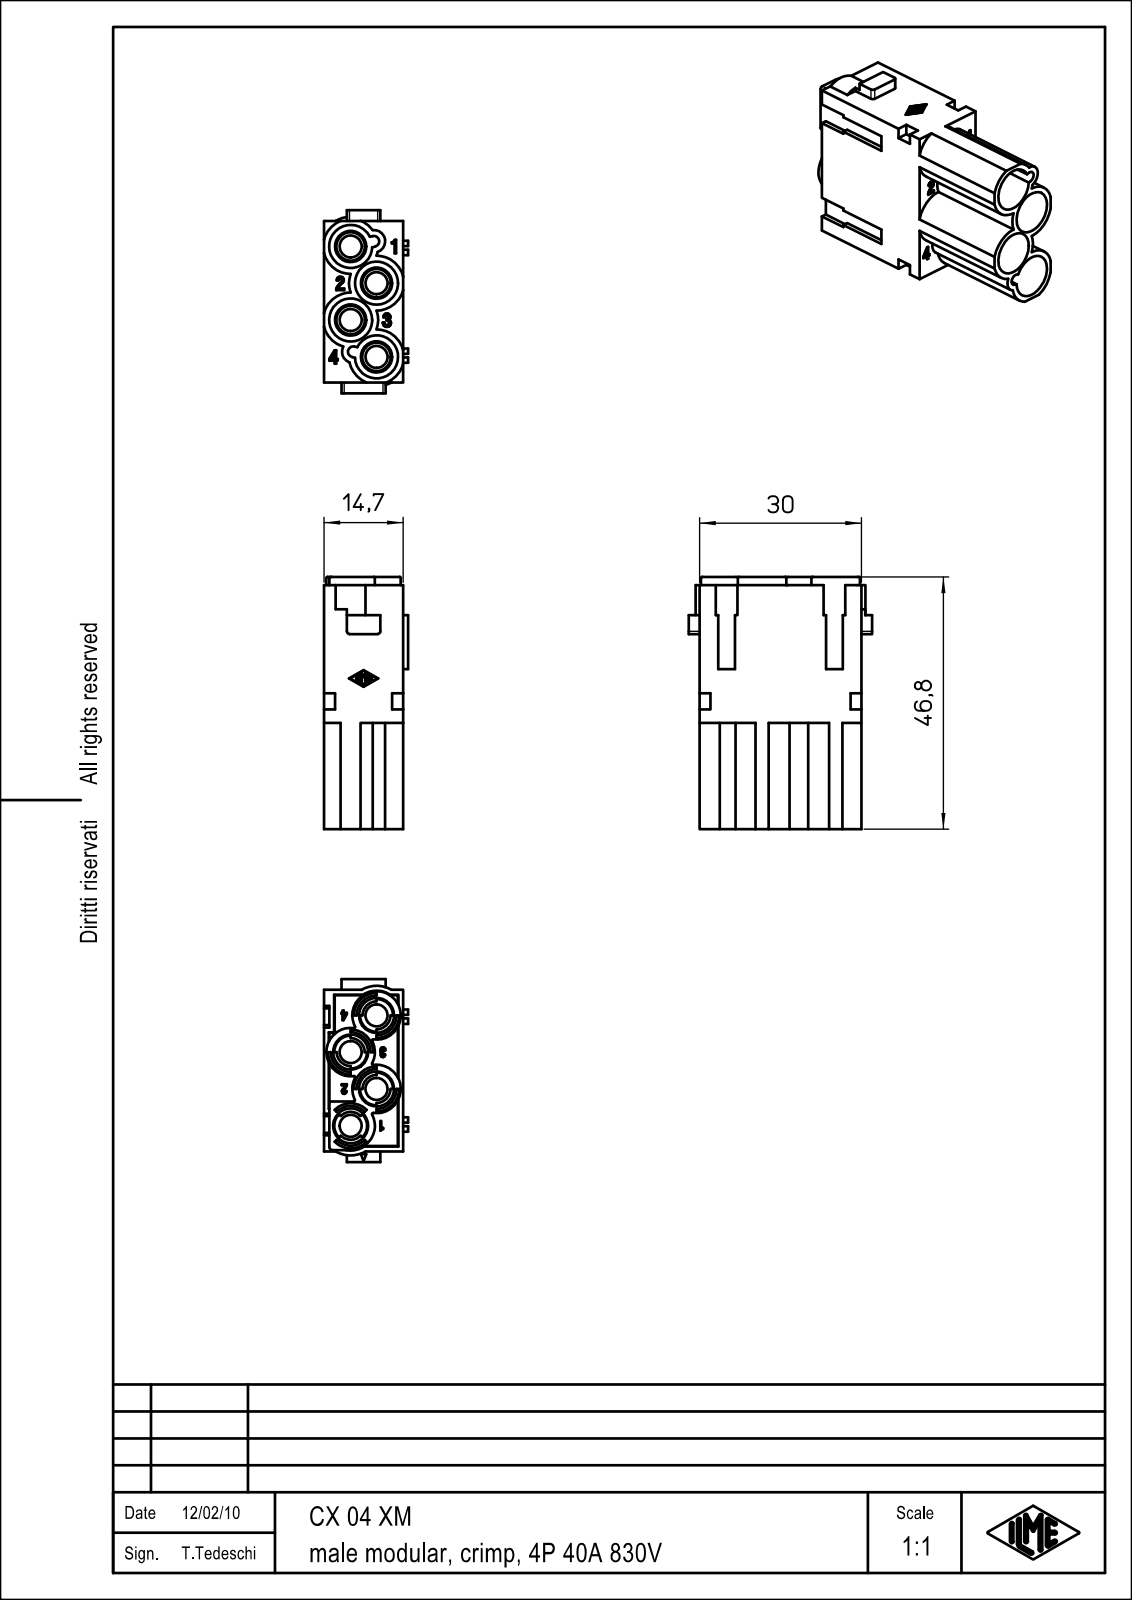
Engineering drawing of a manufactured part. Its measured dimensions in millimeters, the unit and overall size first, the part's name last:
Units: millimetres
Overall size (bounding box): 46.8 × 34 × 15.6
Round holes (diameter × count): ⌀4.1 ×4, ⌀6.5 ×4
Round bosses / shafts (diameter × count): ⌀9 ×1
Partial cylindrical surfaces — rounded edges, fillets, slot ends (radius × count): R0.1 ×5, R0.5 ×5, R3.7 ×4, R4.2 ×4, R4.3 ×4, R5.1 ×4, R4.5 ×3, R0.2 ×2
Main face-to-face distances: 14.7, 30, 1, 13.7, 0.9, 1.8, 12.8, 25.6, 6.4, 45.3
Hole centre spacings: 8.35, 8.36, 13.66, 13.67, 21.05
Volume: 10 454 mm³ · Surface area: 11 671 mm²
Bodies: 1 solid, 758 faces (544 planar, 113 cylindrical, 101 other)
Part name (STEP PRODUCT): CX_04_XM
STEP written by: CoCreate Modeling 16.00A 16-Aug-2008 (C) Parametric Technology GmbH (AUTOMOTIVE_DESIGN)
